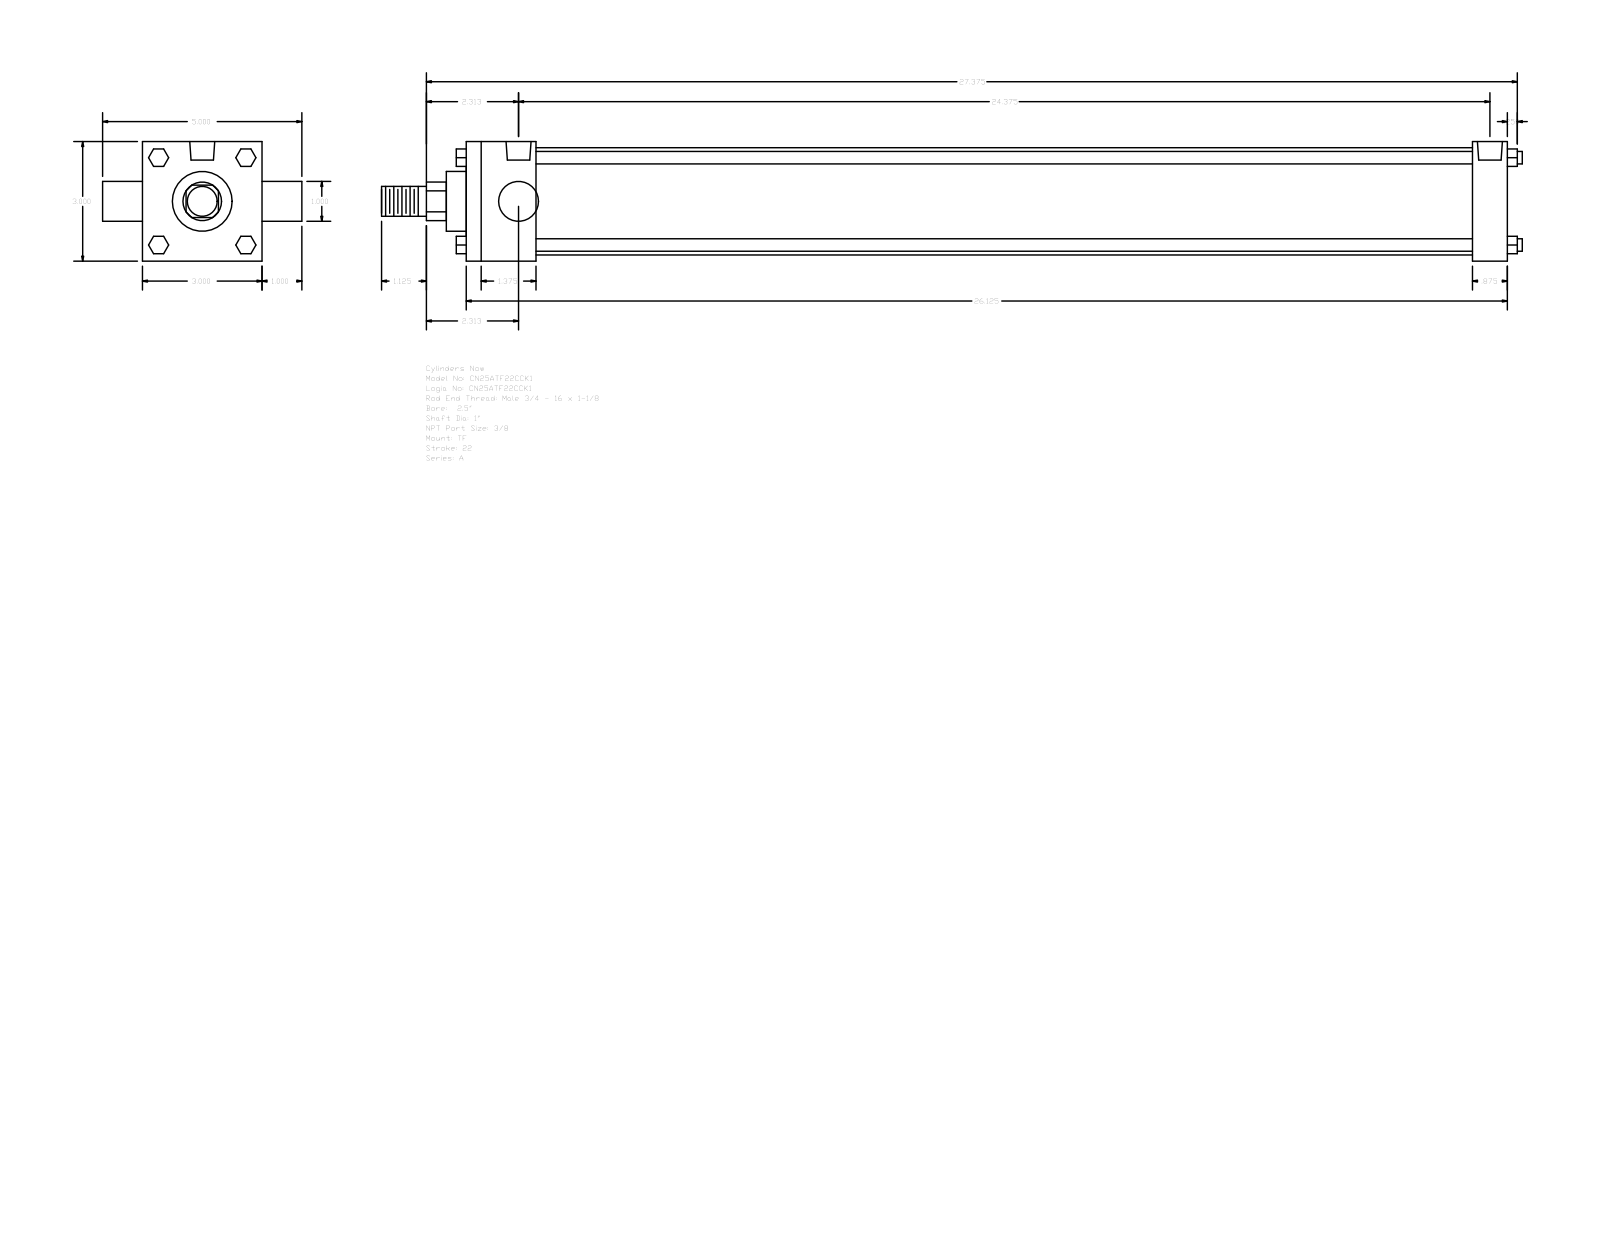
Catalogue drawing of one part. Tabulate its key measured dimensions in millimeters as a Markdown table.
| quantity | value |
| --- | --- |
| part name | A_TF__0250_1 |
| STEP written by | GSSL Pune (CONFIG_CONTROL_DESIGN) |
| units | millimeters |
| bodies | 0 solids, 120 faces (92 planar, 28 cylindrical, 0 other) |
| overall size | 727.08 × 127 × 76.2 |
| round holes (diameter × count) | 5.56 × 3, 15.93 × 2 |
| round bosses / shafts (diameter × count) | 7.94 × 4, 25.4 × 2, 68.33 × 1, 38.1 × 1, 19.05 × 1 |
| partial cylindrical surfaces (radius × count) | 12.29 × 1 |
| main face-to-face distances | 76.2, 663.58, 44.45, 641.35, 596.9, 619.13, 22.23, 25.4, 101.6, 676.28 |
| hole center spacings | 2.38, 621.5, 619.12, 623.88 |
